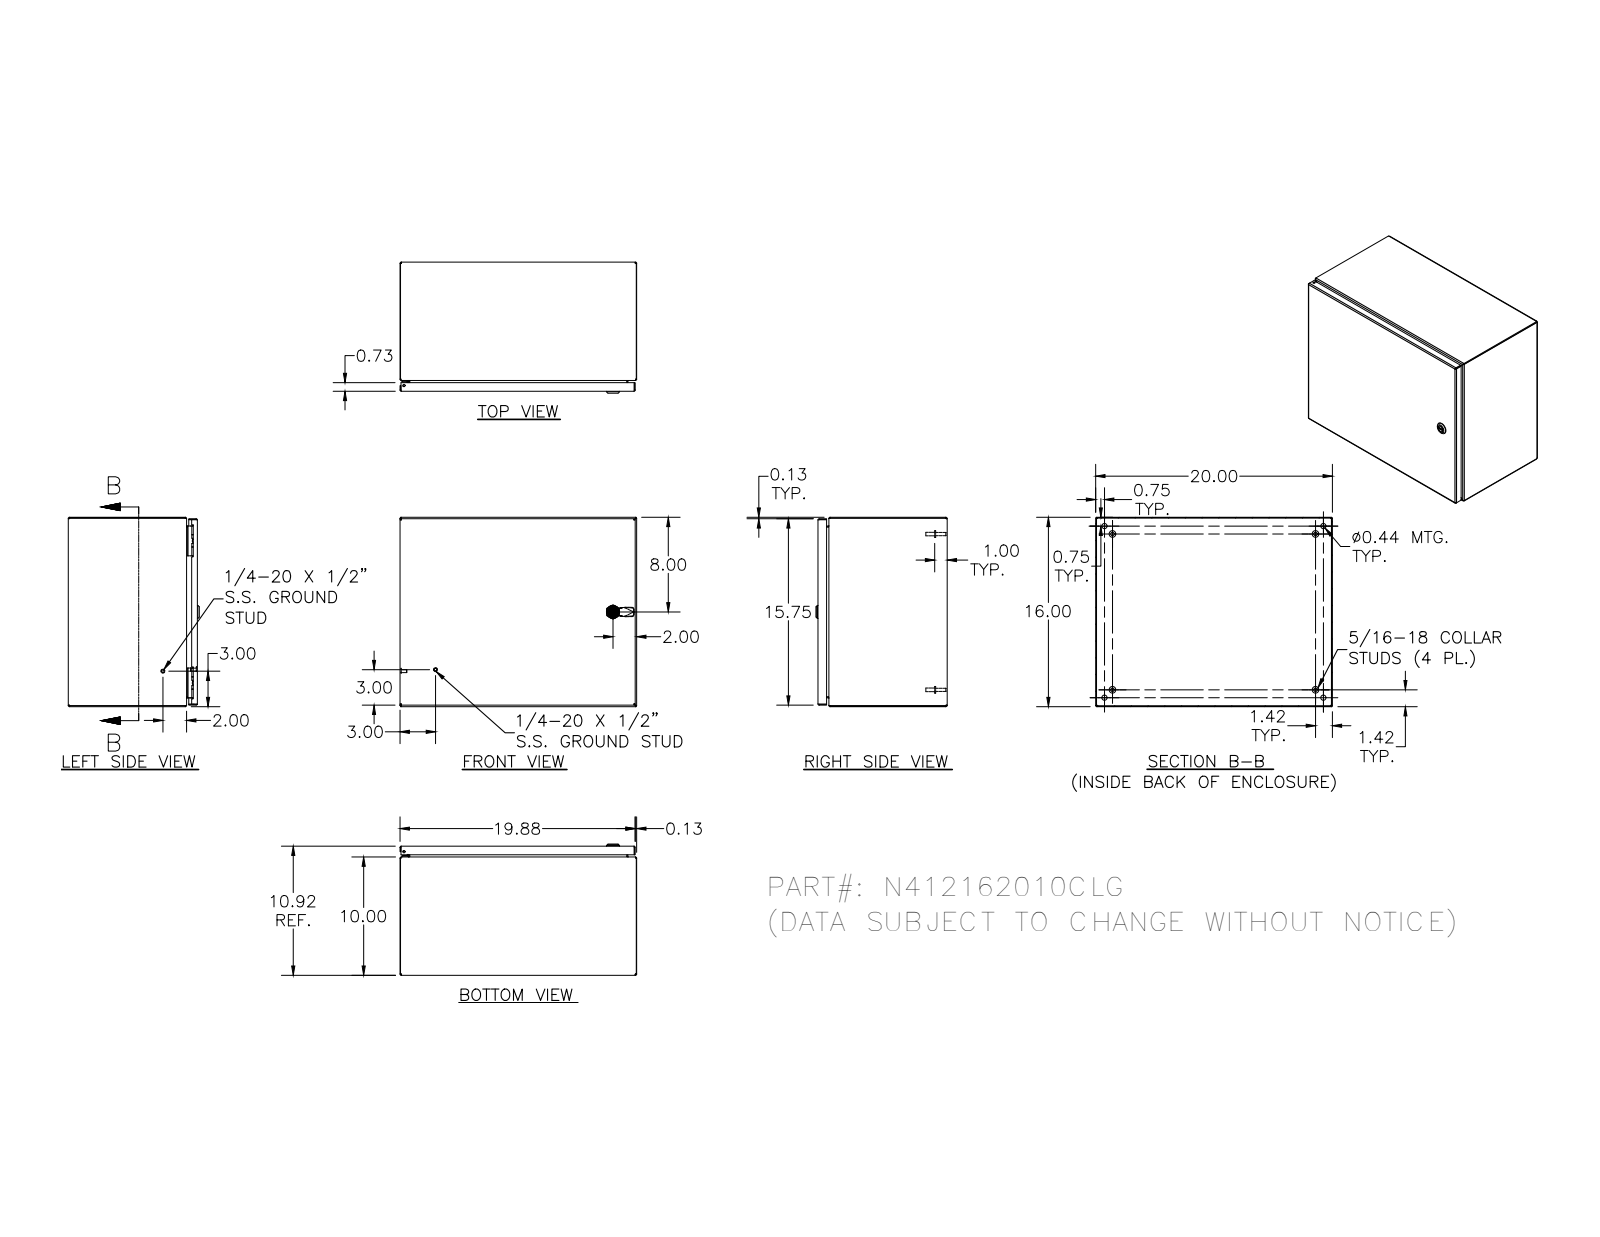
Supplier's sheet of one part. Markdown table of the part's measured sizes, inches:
| quantity | value |
| --- | --- |
| part name | N412162010CLG |
| STEP written by | SolidWorks 2018 (AUTOMOTIVE_DESIGN) |
| units | inches |
| bodies | 33 solids, 1449 faces (530 planar, 547 cylindrical, 372 other) |
| overall size | 20 × 16 × 11.075 |
| volume | 111.6 in³ |
| surface area | 3 035 in² |
| round holes (diameter × count) | 0.188 × 5, 0.093 × 4, 0.152 × 4, 0.167 × 4, 0.172 × 4, 0.437 × 4, 0.156 × 2, 0.187 × 1, 0.197 × 1, 0.315 × 1, 0.394 × 1, 0.402 × 1 |
| round bosses / shafts (diameter × count) | 0.25 × 10, 0.563 × 4, 0.36 × 4, 0.32 × 4, 0.3 × 4, 0.275 × 4, 0.256 × 4, 0.164 × 4 |
| partial cylindrical surfaces (radius × count) | 0.012 × 30, 0.031 × 30, 0.05 × 26, 0.105 × 20, 0.016 × 18, 0.125 × 16, 0.02 × 13, 0.032 × 8 |
| main face-to-face distances | 0.074, 10.843, 0.074, 10.769, 10.917, 15.926, 16, 15.852, 15.926, 19.926 |
| hole center spacings | 12, 0.66, 0.656, 1.307, 1.965, 11.34, 12.66, 0.5 |
